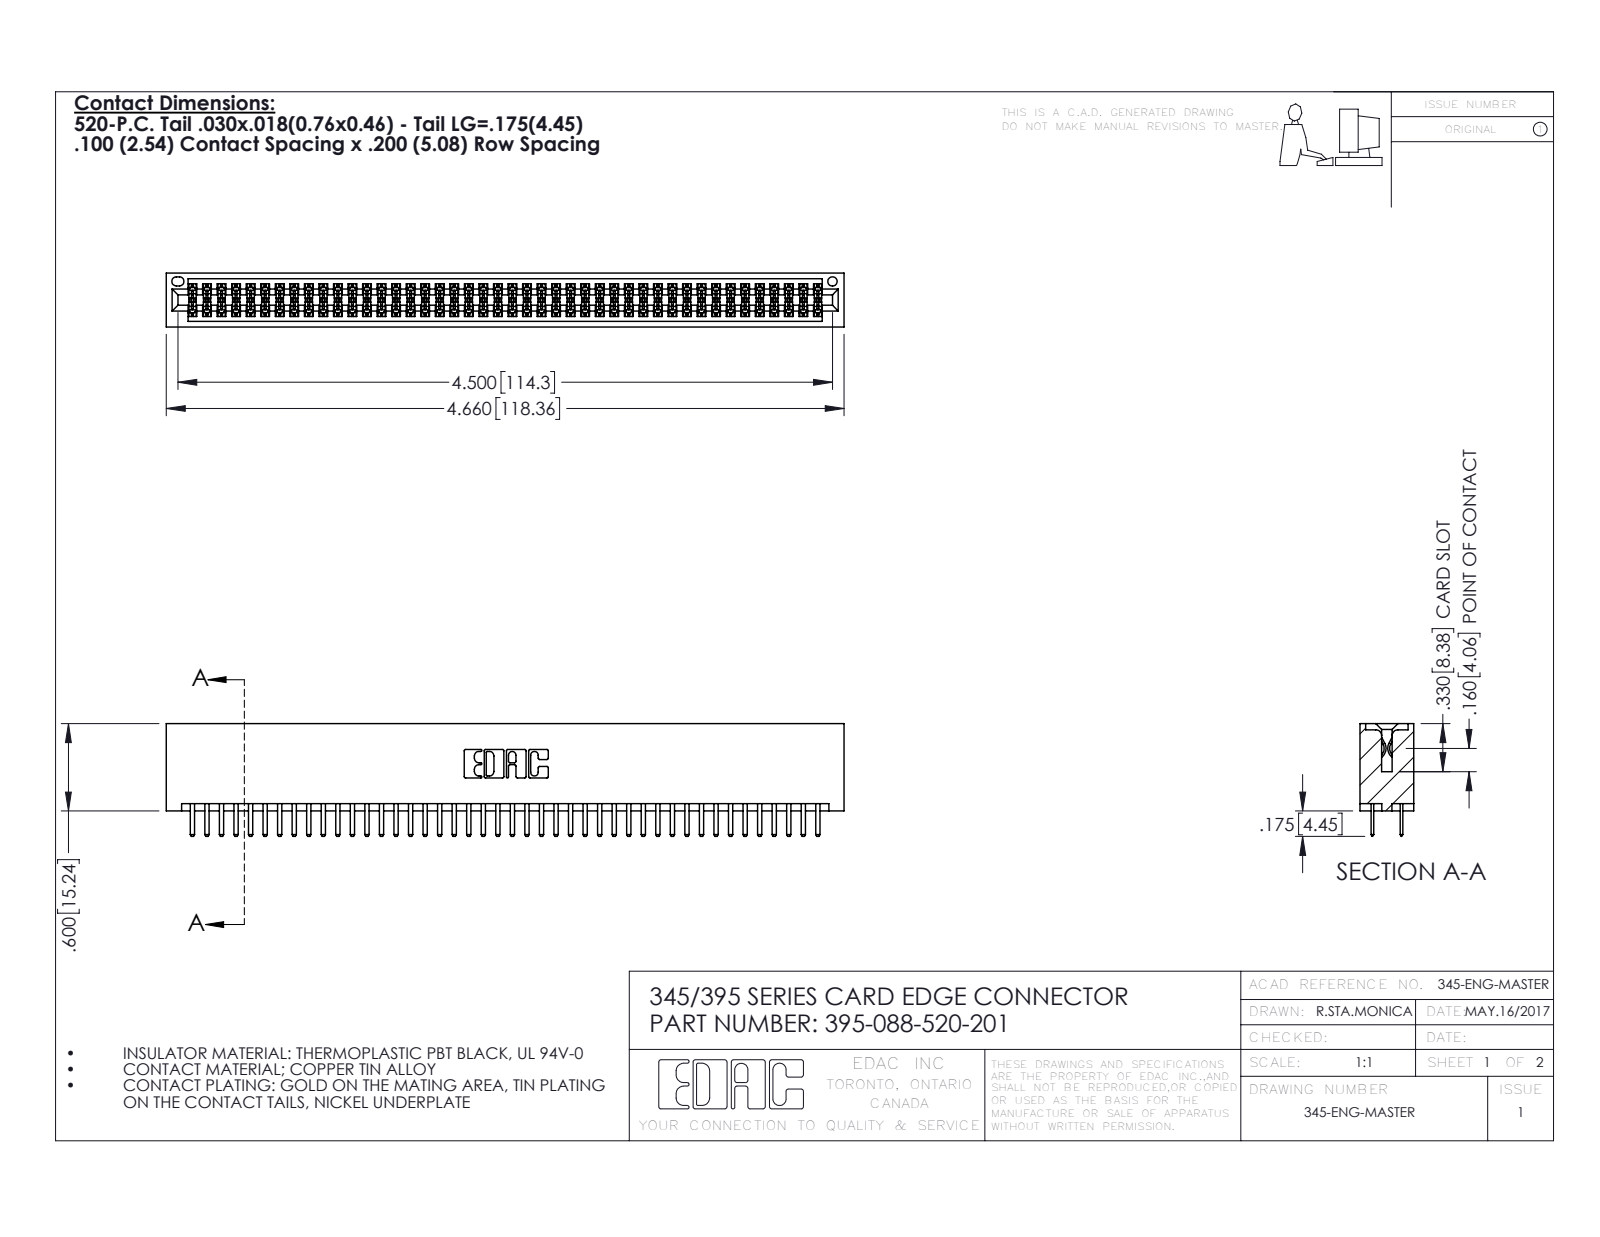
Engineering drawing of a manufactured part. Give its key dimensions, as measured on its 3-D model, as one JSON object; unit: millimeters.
{"part_name": "395-088-520-201; 345 Part_No Mounting Lugs; 345-292-001_345-293-120", "step_written_by": "SolidWorks 2016 (CONFIG_CONTROL_DESIGN)", "units": "millimeters", "bodies": {"solids": 89, "faces": 4870, "planar": 3156, "cylindrical": 1714, "other": 0}, "overall_size": [118.4, 19.7, 9.4], "volume_mm3": 12100, "surface_area_mm2": 18140, "round_holes": [[1.6, 1]], "partial_cylinders_radius": [[0.2, 132], [0.3, 92], [0.3, 22], [0.2, 6], [0.8, 6], [0.7, 3], [0.4, 2], [0.5, 2]], "face_to_face_distances": [7.6, 1.8, 5.1, 9.4, 2.5, 6.9, 0.6, 5.7, 0.6, 1.8]}
